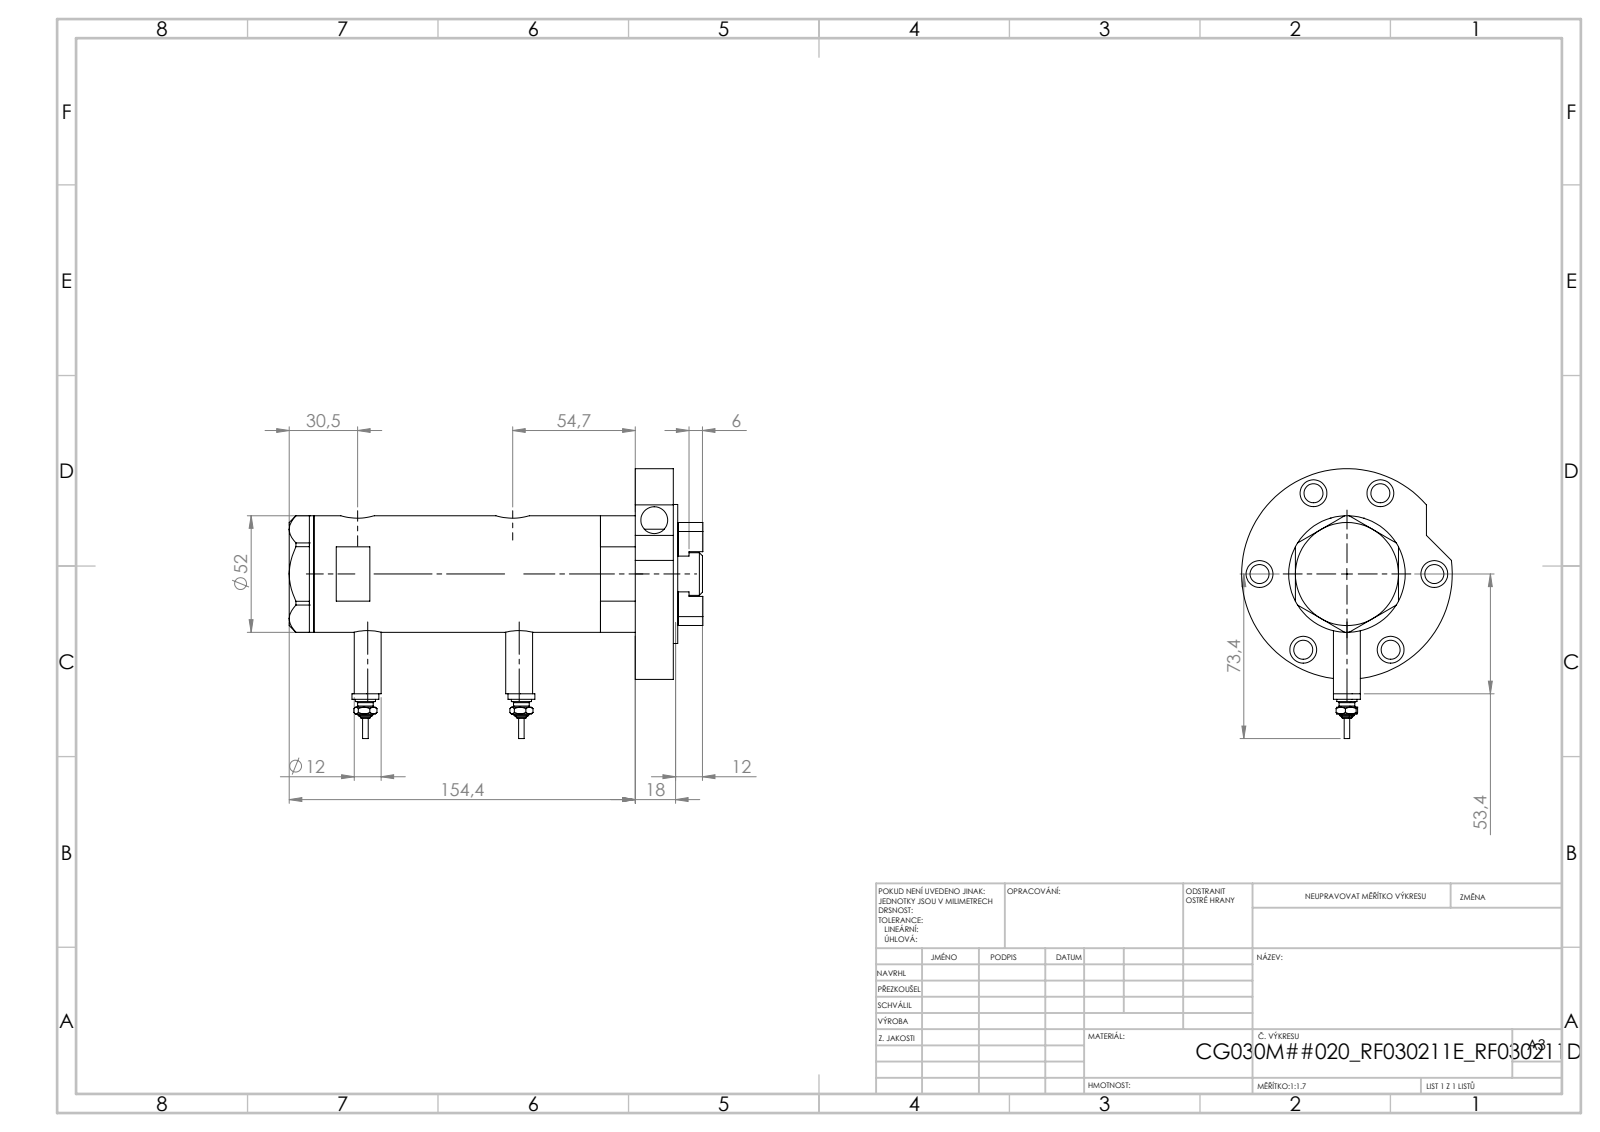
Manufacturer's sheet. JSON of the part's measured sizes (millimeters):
{"part_name": "Switch; V270CG_RF211E; V270CG_BACK; V270CG_FRONT (+3 more)", "step_written_by": "SolidWorks 2019 (CONFIG_CONTROL_DESIGN)", "units": "millimeters", "bodies": {"solids": 9, "faces": 310, "planar": 128, "cylindrical": 118, "other": 64}, "overall_size": [184.6, 120.4, 94], "volume_mm3": 430950, "surface_area_mm2": 107428, "round_holes": [[12, 7], [8.5, 6], [5.1, 4], [9, 4], [9.73, 2], [12.5, 2], [15, 2], [6.5, 1], [20, 1], [21.5, 1], [30, 1], [33, 1]], "round_bosses_or_shafts": [[12, 4], [9, 2], [7, 2], [4.5, 2], [2.5, 2], [94, 1], [62, 1], [52, 1]], "face_to_face_distances": [17, 143.4, 160.4, 2, 11, 162.4, 91.5, 51.9, 68.9, 173.4], "hole_center_spacings": [39, 16.74, 37.57, 46.81, 10, 22.37, 22.95, 28.26]}
